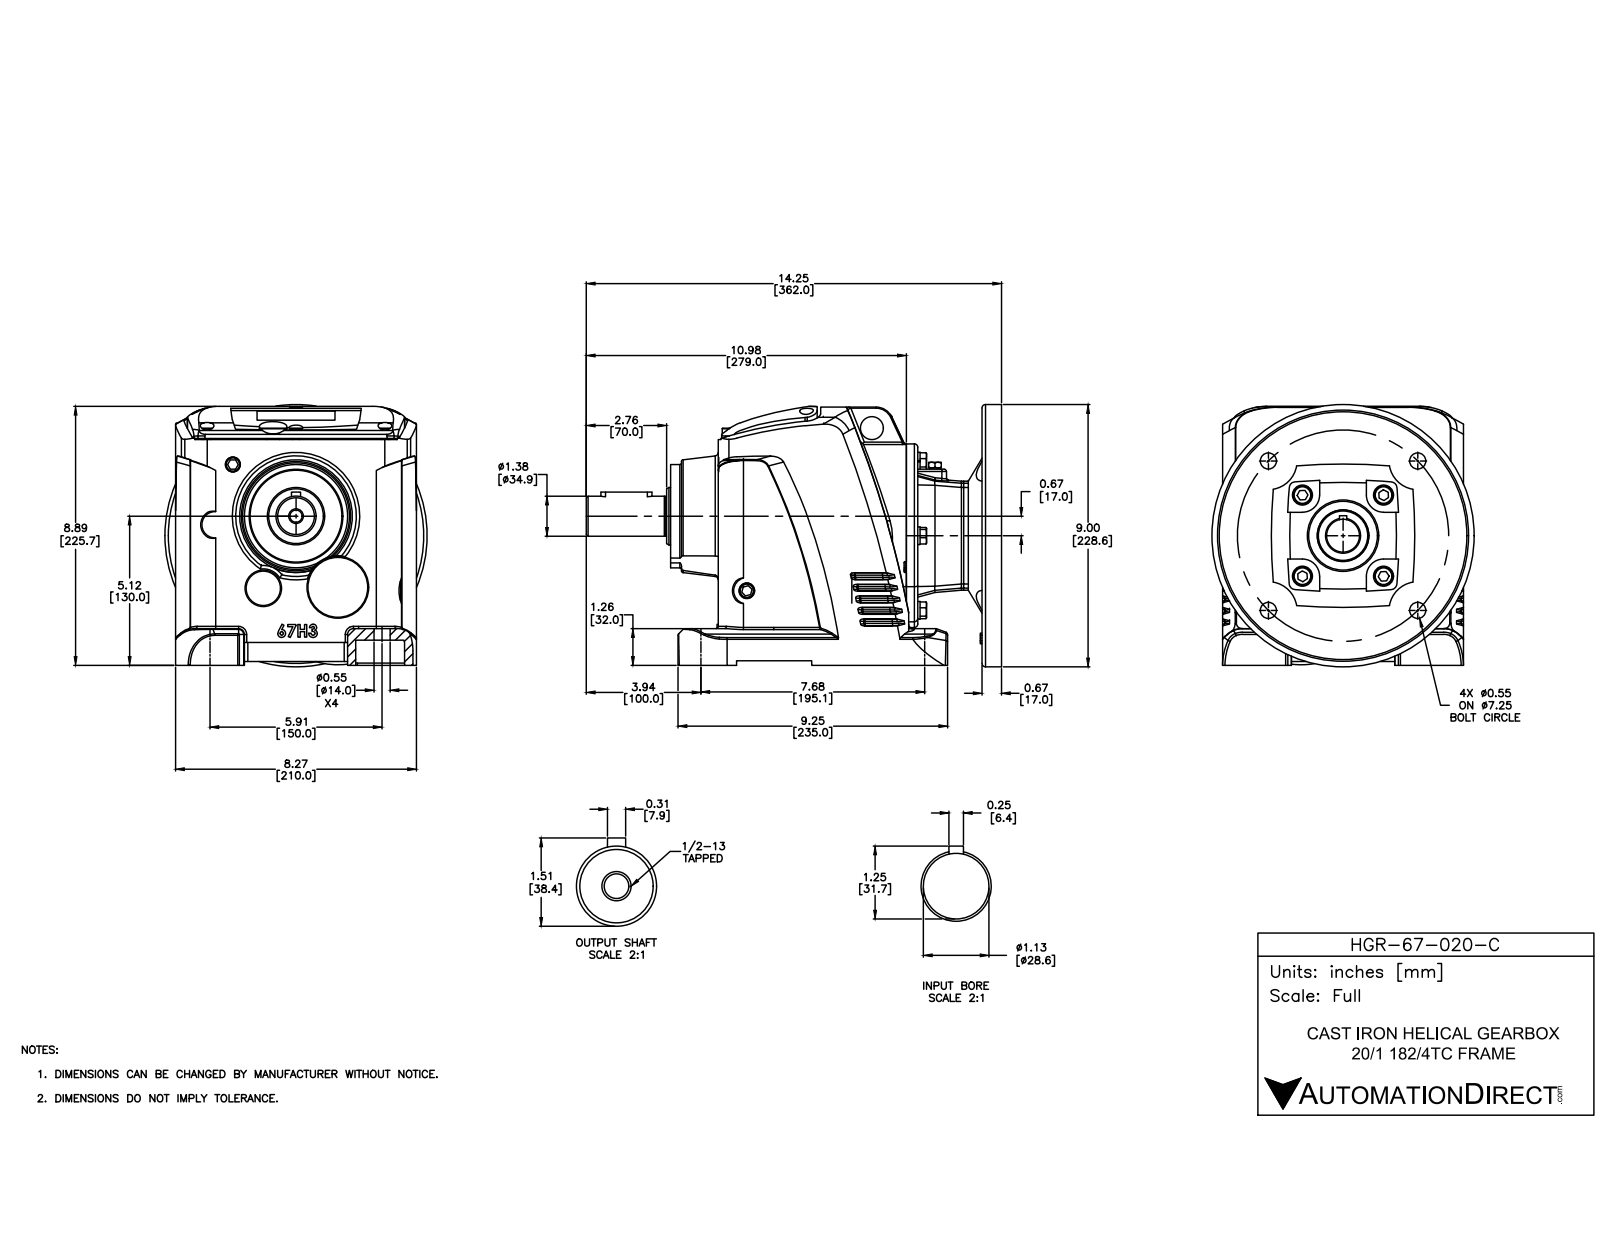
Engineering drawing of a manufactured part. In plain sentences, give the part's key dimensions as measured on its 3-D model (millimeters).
The part is named "HGR-67-005-C". Its 3-D file was written by "SolidWorks 2015 (CONFIG_CONTROL_DESIGN)". It is 16 solids with 1054 faces: 350 planar, 267 cylindrical and 437 other. Overall it measures 362 by 228.6 by 228.6 millimeters. Its volume is 7 335 000 cubic millimeters and its surface area 558 500 square millimeters. Round holes: 8 of diameter 14, 6 of diameter 12, 4 of diameter 17.5, 1 of diameter 4.1, 1 of diameter 10.7, 1 of diameter 20, 1 of diameter 28.6, 1 of diameter 45, 1 of diameter 50, 1 of diameter 215.9. Round bosses or shafts: 4 of diameter 16, 4 of diameter 15.4, 4 of diameter 12.6, 3 of diameter 10, 1 of diameter 228.6, 1 of diameter 160, 1 of diameter 90, 1 of diameter 80. Partial cylindrical surfaces (rounded edges, fillets, slot ends): 43 of radius 2, 7 of radius 5, 6 of radius 4, 6 of radius 15, 6 of radius 25, 5 of radius 3, 4 of radius 1, 4 of radius 17.5. The main face-to-face distances are 77.9, 1, 11.9, 66, 197, 241.9, 230, 164, 13, 47. The hole center spacings are 104.8, 42.1, 50, 70.7, 92.1, 130.2, 142.1, 29.1.
